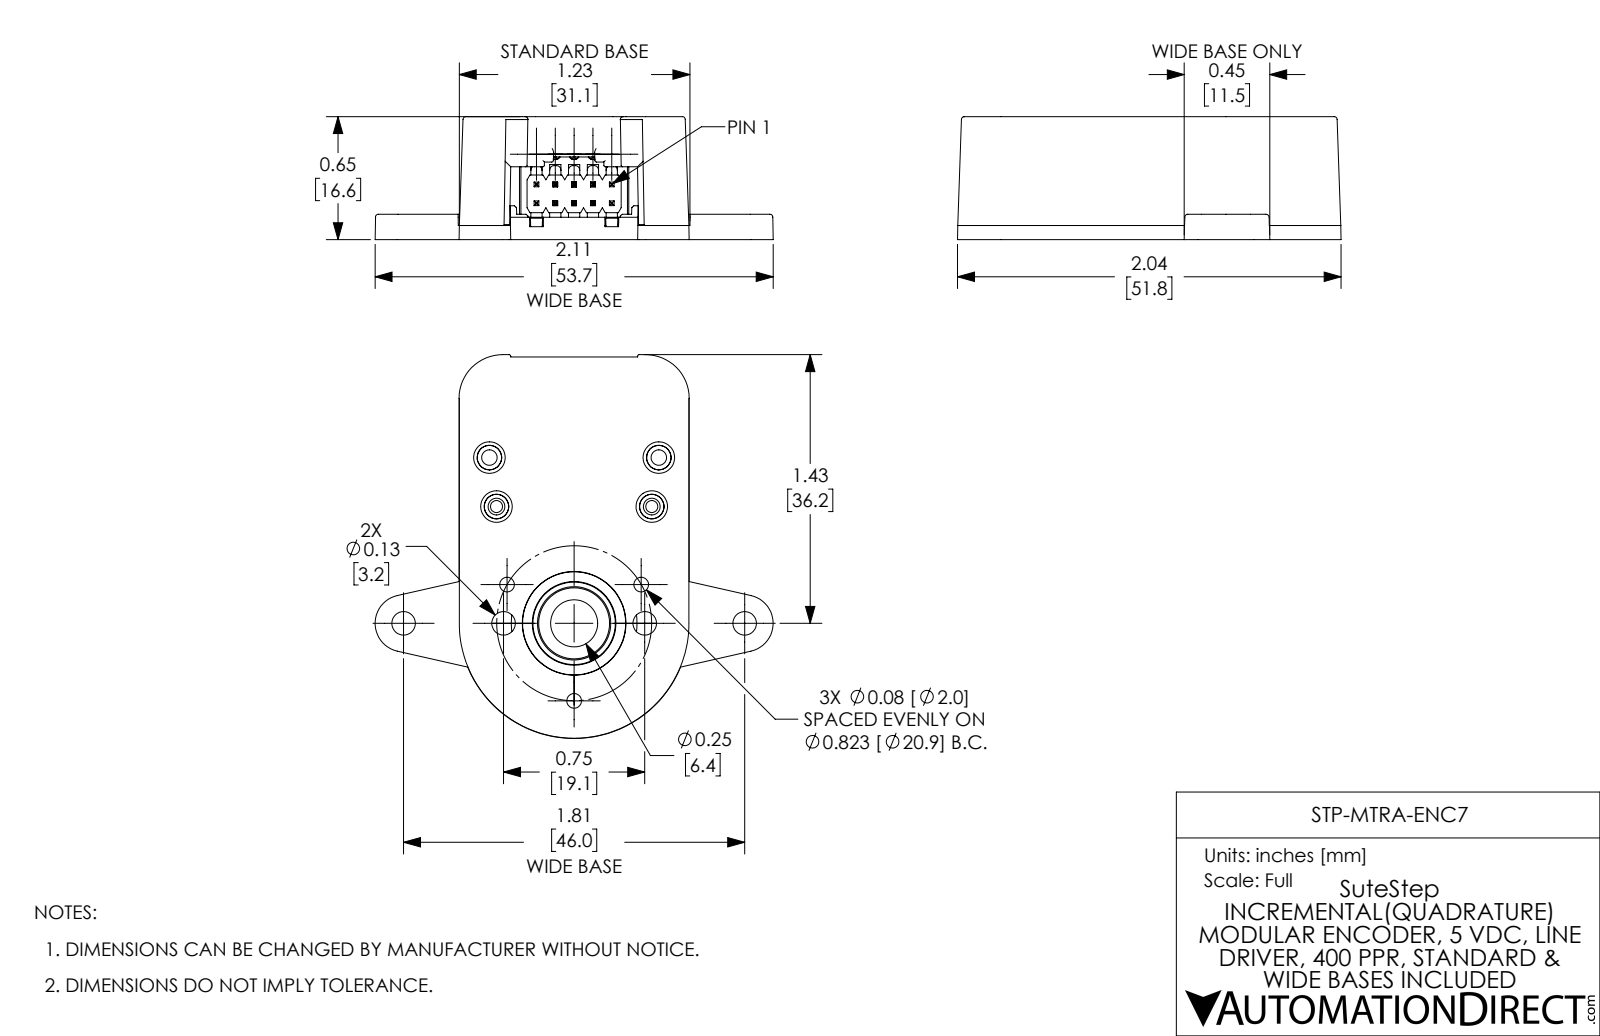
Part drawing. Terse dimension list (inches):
name: STP-MTRA-ENC7
written by: SolidWorks 2017 (AUTOMOTIVE_DESIGN)
unit: in
bodies: 32 solids, 2929 faces (1428 planar, 762 cylindrical, 739 other)
size: 3.585 × 2.111 × 0.653
volume: 1.197 in³; area: 32.01 in²
holes: 8× ⌀0.13, 6× ⌀0.078, 5× ⌀0.032, 4× ⌀0.089, 4× ⌀0.125, 2× ⌀0.109, 1× ⌀0.093, 1× ⌀0.095, 1× ⌀0.095, 1× ⌀0.25
bosses: 5× ⌀0.078, 4× ⌀0.187, 4× ⌀0.16, 2× ⌀0.219, 2× ⌀0.195, 2× ⌀0.112, 2× ⌀0.105, 1× ⌀1
rounds: 46× R0.025, 41× R0.016, 16× R0.008, 14× R0.005, 12× R0.031, 10× R0.02, 6× R0.015, 6× R0.03
face distances: 0.135, 0.125, 0.653, 0.643, 0.518, 0.54, 0.06, 0.113, 0.53, 0.405
hole spacings: 1.918, 0.713, 0.1, 0.418, 0.873, 0.883, 1.111, 0.2
